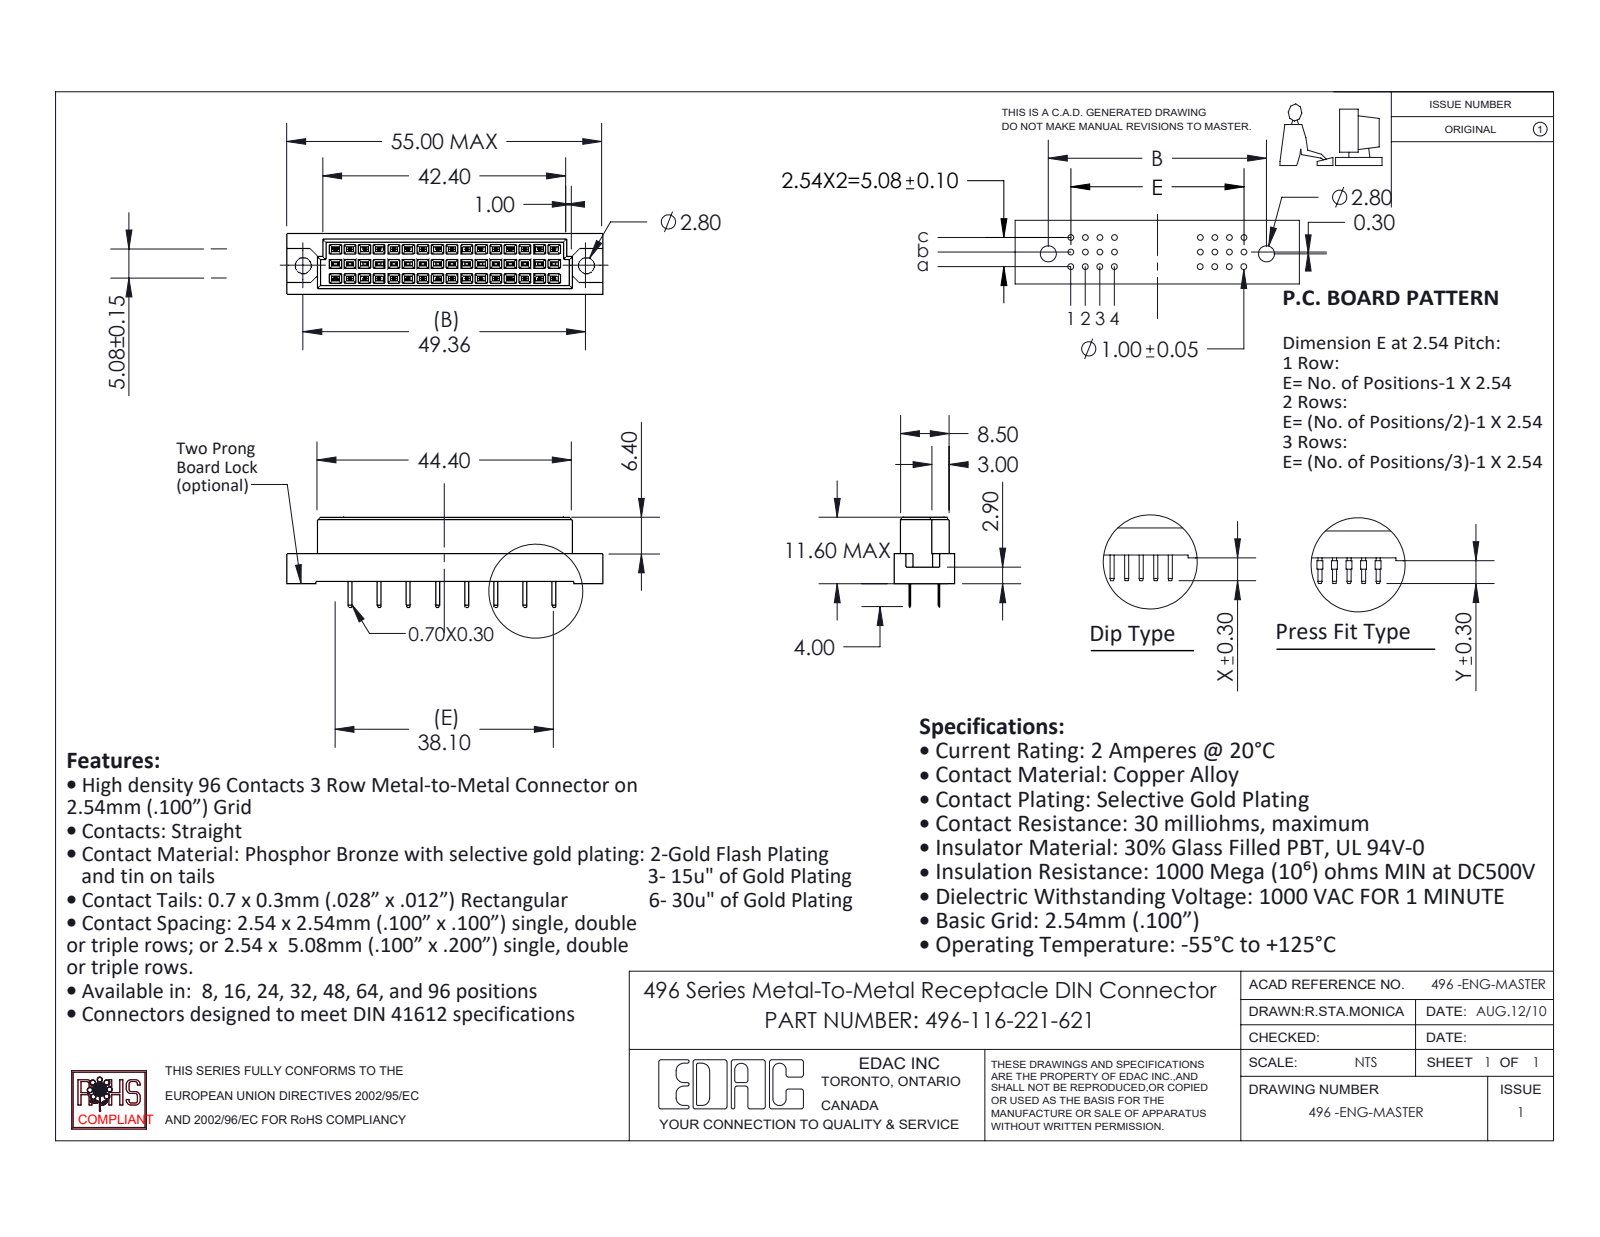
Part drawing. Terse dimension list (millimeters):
name: 496 Part_48; 496-116-221-621; 496-290_21
written by: SolidWorks 2020 (CONFIG_CONTROL_DESIGN)
unit: mm
bodies: 17 solids, 826 faces (822 planar, 4 cylindrical, 0 other)
size: 55 × 15.6 × 10.6
volume: 4 618 mm³; area: 4 487 mm²
holes: 2× ⌀2.8
face distances: 2.54, 5.08, 1.05, 9.55, 0.81, 10.6, 0.56, 3.35, 1.73, 8.5
hole spacings: 49.36
